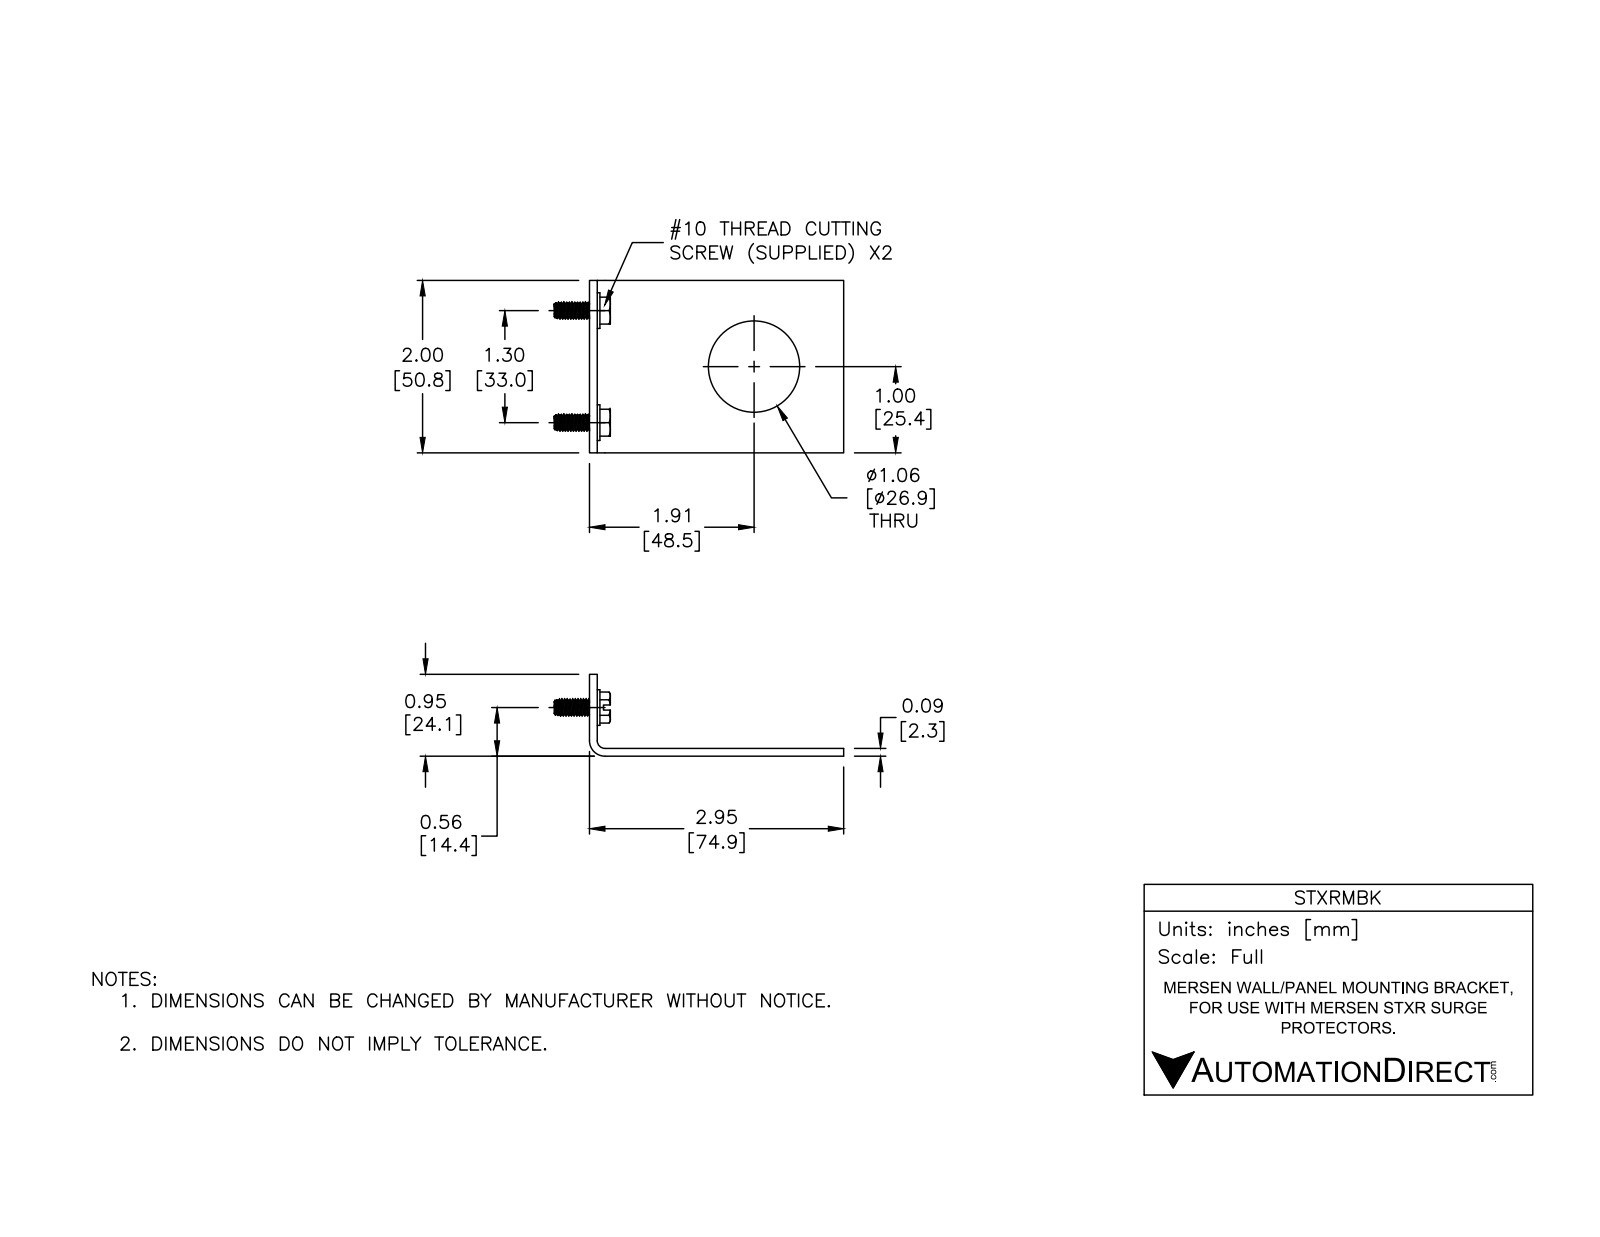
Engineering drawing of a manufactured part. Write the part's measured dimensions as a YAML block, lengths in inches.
part_name: "STXRMBK"
step_written_by: "SolidWorks 2016 (AUTOMOTIVE_DESIGN)"
units: inches
bodies: {solids: 3, faces: 384, planar: 138, cylindrical: 122, other: 124}
overall_size: [3.36, 2, 0.95]
volume: 0.638
surface_area: 16.41
round_holes:
  - {diameter: 0.2, count: 2}
  - {diameter: 1.06, count: 1}
round_bosses_or_shafts:
  - {diameter: 0.414, count: 2}
  - {diameter: 0.19, count: 2}
  - {diameter: 0.149, count: 2}
partial_cylinders:
  - {radius: 0.09, count: 1}
  - {radius: 0.18, count: 1}
face_to_face_distances: [0.09, 2, 0.95, 0.86, 2.86, 2.95, 0.313, 2.83, 0.03, 0.12]
hole_center_spacings: [1.3]
